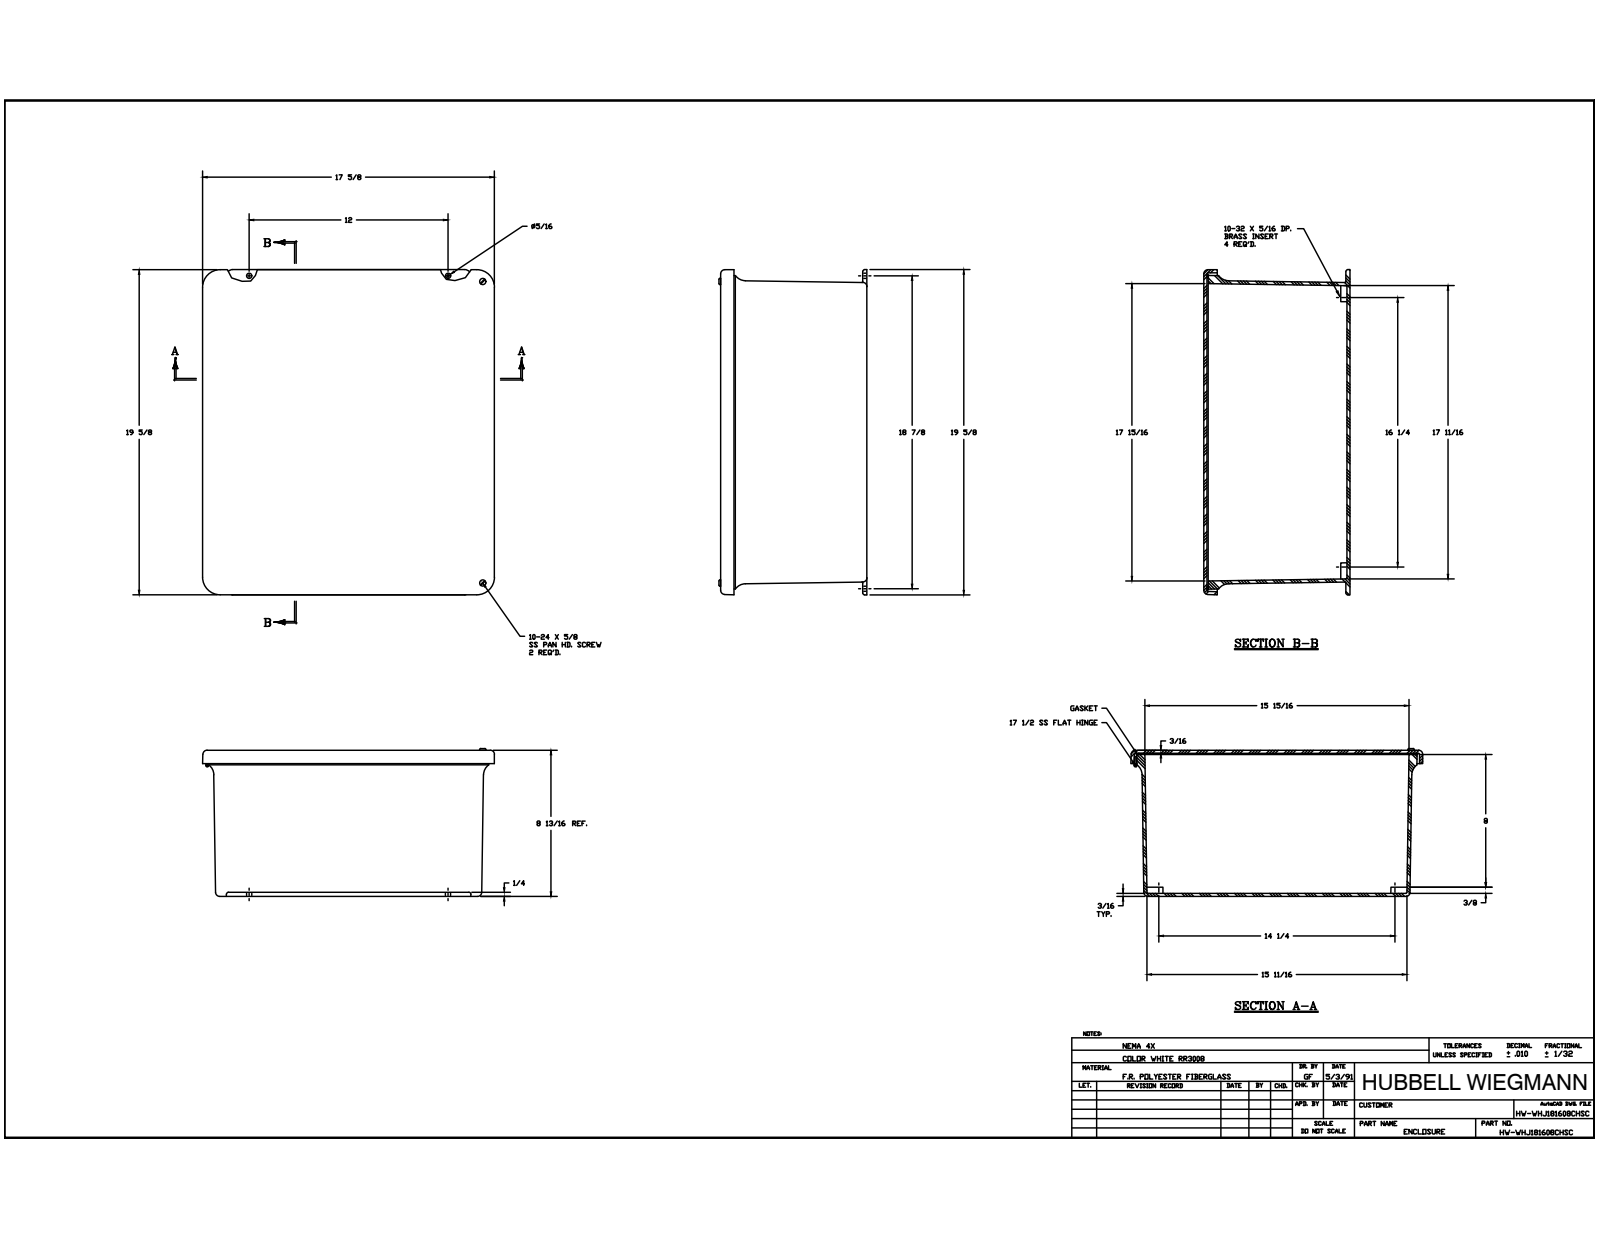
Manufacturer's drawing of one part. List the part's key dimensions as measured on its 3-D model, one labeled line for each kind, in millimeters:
Part name (STEP PRODUCT): J1816HW_1; RMINS45821P_69; RMINS45821P_70; RMINS45821P_71 (+8 more)
STEP written by: Autodesk Inventor 2014 (AUTOMOTIVE_DESIGN)
Units: millimetres
Bodies: 26 solids, 945 faces (369 planar, 367 cylindrical, 209 other)
Overall size (bounding box): 498.48 × 448.11 × 227.5
Volume: 4 254 000 mm³ · Surface area: 1 741 000 mm²
Round holes (diameter × count): ⌀3.33 ×12, ⌀3.56 ×12, ⌀3.86 ×5, ⌀3.96 ×4, ⌀5.54 ×4, ⌀3.68 ×2, ⌀2.16 ×1, ⌀2.16 ×1
Round bosses / shafts (diameter × count): ⌀6.35 ×12, ⌀3.17 ×12, ⌀6.86 ×6, ⌀4.83 ×2, ⌀3.97 ×2, ⌀3.94 ×1
Partial cylindrical surfaces — rounded edges, fillets, slot ends (radius × count): R0.79 ×20, R3.17 ×12, R6.35 ×8, R5.08 ×4, R9.53 ×4, R19.05 ×4, R1.6 ×2
Main face-to-face distances: 4.76, 219.41, 224.17, 4.77, 214.64, 219.4, 7.68, 12.44, 217.49, 212.72
Hole centre spacings: 85.72, 85.73, 171.45, 260.35, 6.35, 247.65, 254, 34.8
